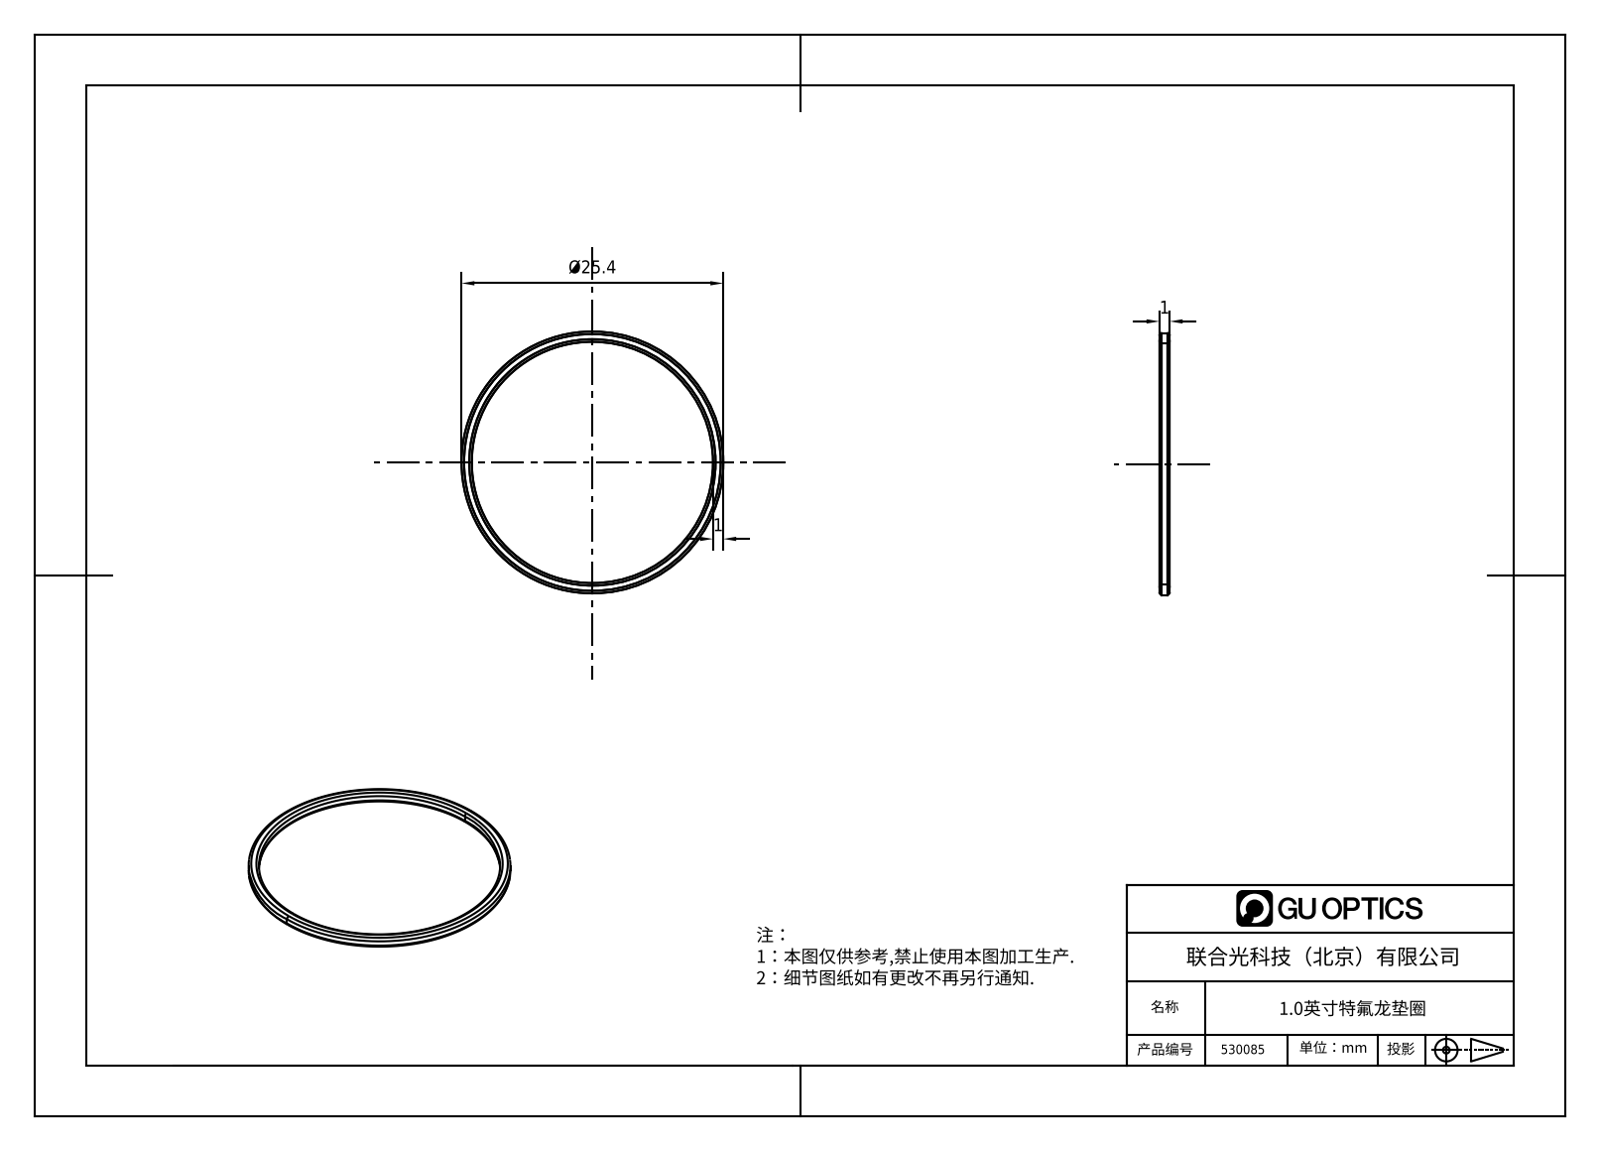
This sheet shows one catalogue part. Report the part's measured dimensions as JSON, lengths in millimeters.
{"part_name": "1.8.5.24_ZFK-D1.0_1.0英寸特氟龙垫圈", "step_written_by": "SolidWorks 2018 (CONFIG_CONTROL_DESIGN)", "units": "millimeters", "bodies": {"solids": 1, "faces": 14, "planar": 2, "cylindrical": 4, "other": 8}, "overall_size": [25.4, 25.4, 1], "volume_mm3": 73, "surface_area_mm2": 274, "round_holes": [[23.4, 1]], "round_bosses_or_shafts": [[25.4, 1]], "face_to_face_distances": [1]}
